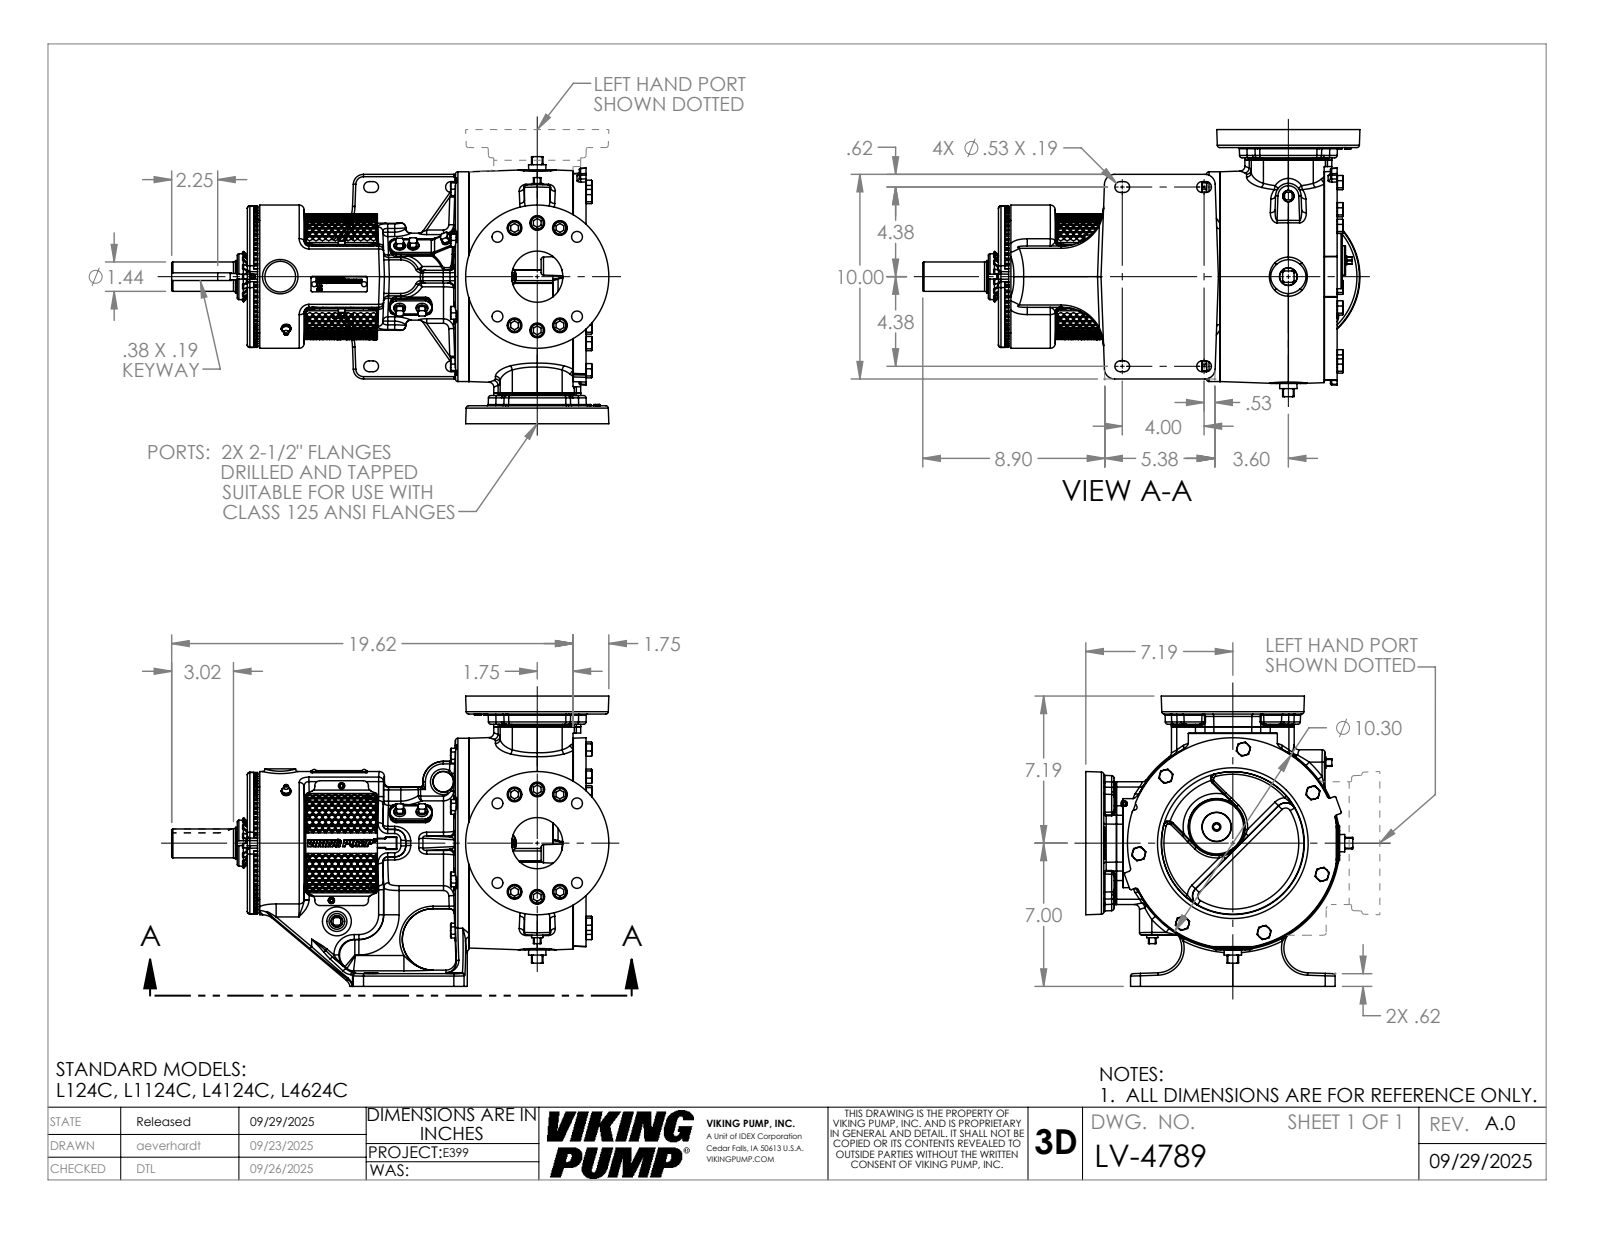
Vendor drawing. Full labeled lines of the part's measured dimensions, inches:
Part name (STEP PRODUCT): LV-4789
STEP written by: SolidWorks 2024 (AUTOMOTIVE_DESIGN)
Units: inches
Bodies: 1 solid, 5213 faces (1519 planar, 987 cylindrical, 2707 other)
Overall size (bounding box): 21.372 × 14.188 × 13.053
Volume: 893.6 in³ · Surface area: 1 320 in²
Round holes (diameter × count): ⌀0.719 ×12, ⌀0.531 ×8, ⌀1.094 ×8, ⌀0.199 ×6, ⌀0.25 ×6, ⌀0.159 ×3, ⌀0.129 ×2, ⌀0.266 ×2, ⌀0.313 ×2, ⌀2.5 ×2, ⌀0.453 ×1, ⌀2.44 ×1
Round bosses / shafts (diameter × count): ⌀0.66 ×12, ⌀0.625 ×10, ⌀0.625 ×5, ⌀0.437 ×3, ⌀0.312 ×3, ⌀0.114 ×2, ⌀10.25 ×1, ⌀7 ×1
Partial cylindrical surfaces — rounded edges, fillets, slot ends (radius × count): R0.063 ×109, R0.12 ×78, R0.069 ×74, R0.24 ×48, R0.01 ×34, R0.009 ×28, R0.03 ×18, R0.06 ×18
Main face-to-face distances: 14.187, 13.807, 0.5, 3.537, 10.27, 0.88, 2.25, 2.143, 5.68, 15.95
Hole centre spacings: 3, 2.75, 2.625, 1.375, 0.941, 1.136, 2.06, 2.18
